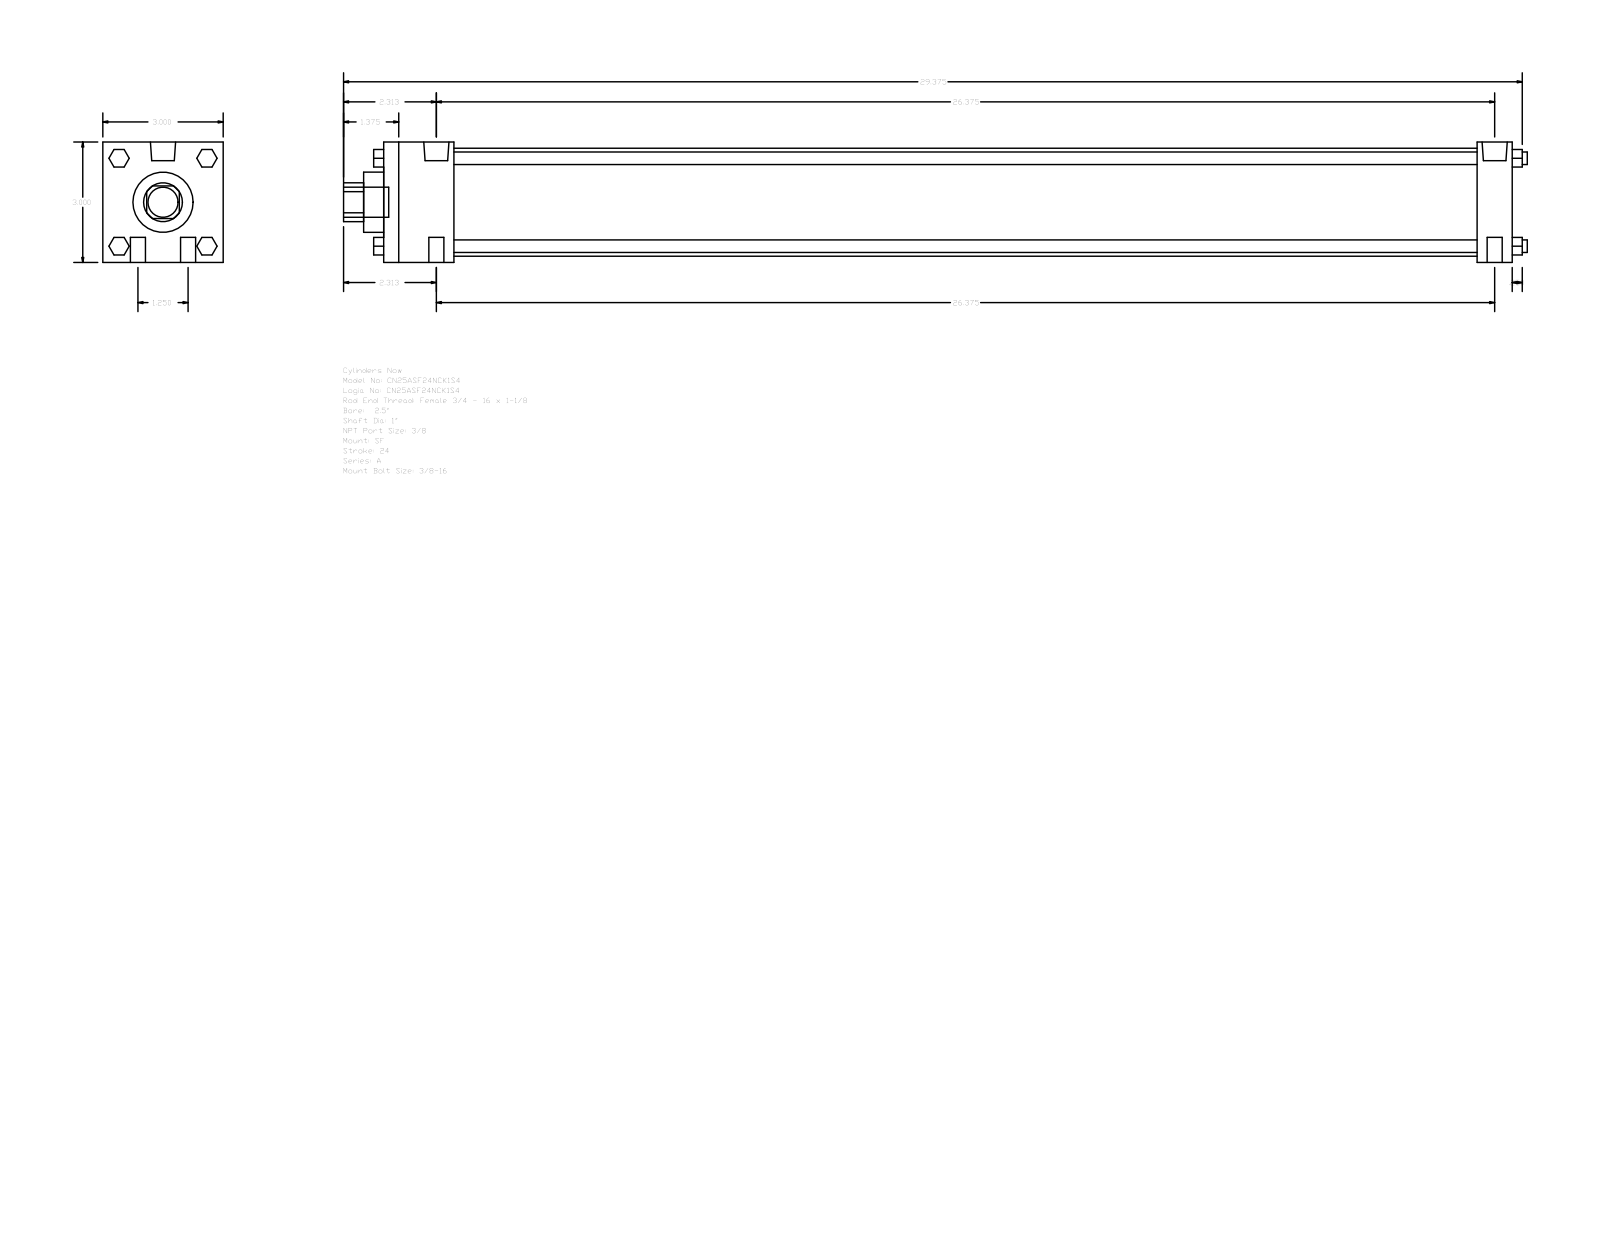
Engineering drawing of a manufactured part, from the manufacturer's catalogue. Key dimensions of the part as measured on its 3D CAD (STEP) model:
Part name (STEP PRODUCT): A_SF__0250_1
STEP written by: GSSL Pune (CONFIG_CONTROL_DESIGN)
Units: millimetres
Bodies: 0 solids, 124 faces (94 planar, 30 cylindrical, 0 other)
Overall size (bounding box): 749.3 × 76.2 × 76.2
Round holes (diameter × count): ⌀25.4 ×1, ⌀38.1 ×1, ⌀68.33 ×1
Round bosses / shafts (diameter × count): ⌀9.53 ×4, ⌀7.94 ×4, ⌀15.93 ×2, ⌀5.56 ×2, ⌀19.05 ×1
Partial cylindrical surfaces — rounded edges, fillets, slot ends (radius × count): R12.29 ×1
Main face-to-face distances: 76.2, 714.37, 692.15, 22.22, 44.45, 647.7, 669.92, 12.7, 727.07, 6.35
